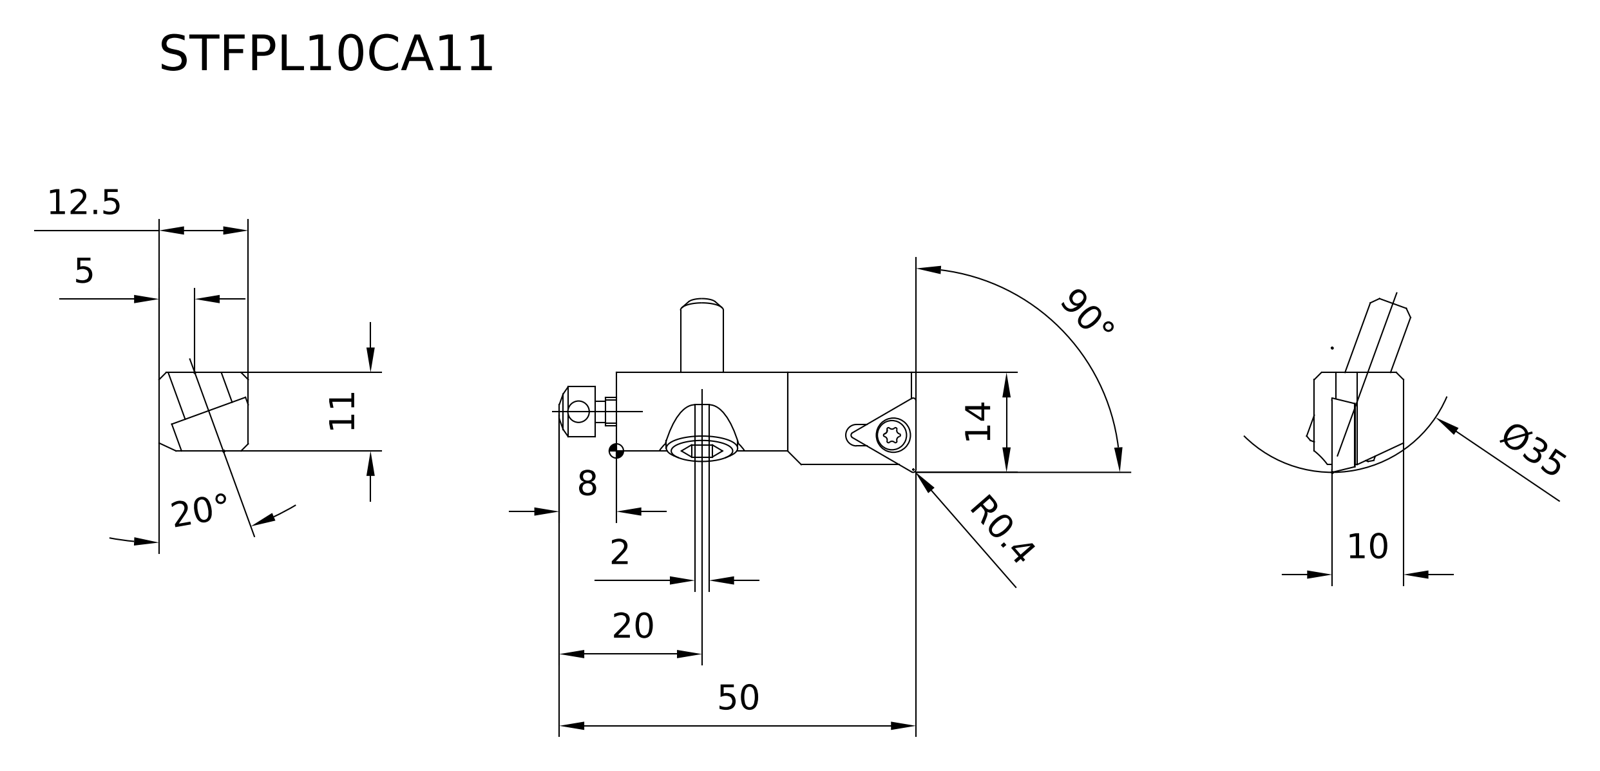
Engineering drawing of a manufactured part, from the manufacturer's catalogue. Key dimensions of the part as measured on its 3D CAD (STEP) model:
Part name (STEP PRODUCT): STFPL10CA11_ASM
STEP written by: SIEMENS PLM Software NX 10.0 (AUTOMOTIVE_DESIGN)
Units: millimetres
Bodies: 5 solids, 142 faces (50 planar, 60 cylindrical, 32 other)
Overall size (bounding box): 49.36 × 23.28 × 14.56
Volume: 5 012 mm³ · Surface area: 3 645 mm²
Round holes (diameter × count): ⌀1.8 ×2, ⌀2.5 ×1, ⌀3.3 ×1, ⌀4.2 ×1
Round bosses / shafts (diameter × count): ⌀3 ×2, ⌀10 ×1, ⌀7 ×1, ⌀6 ×1, ⌀5 ×1, ⌀4.1 ×1, ⌀4 ×1
Partial cylindrical surfaces — rounded edges, fillets, slot ends (radius × count): R0.22 ×6, R0.25 ×6, R0.47 ×6, R0.57 ×6, R3.5 ×2, R5.5 ×2, R1.5 ×1, R10 ×1
Main face-to-face distances: 12.5, 11, 3, 6, 12.92, 1.92, 2.7, 5, 15.2, 1
Hole centre spacings: 39.29
